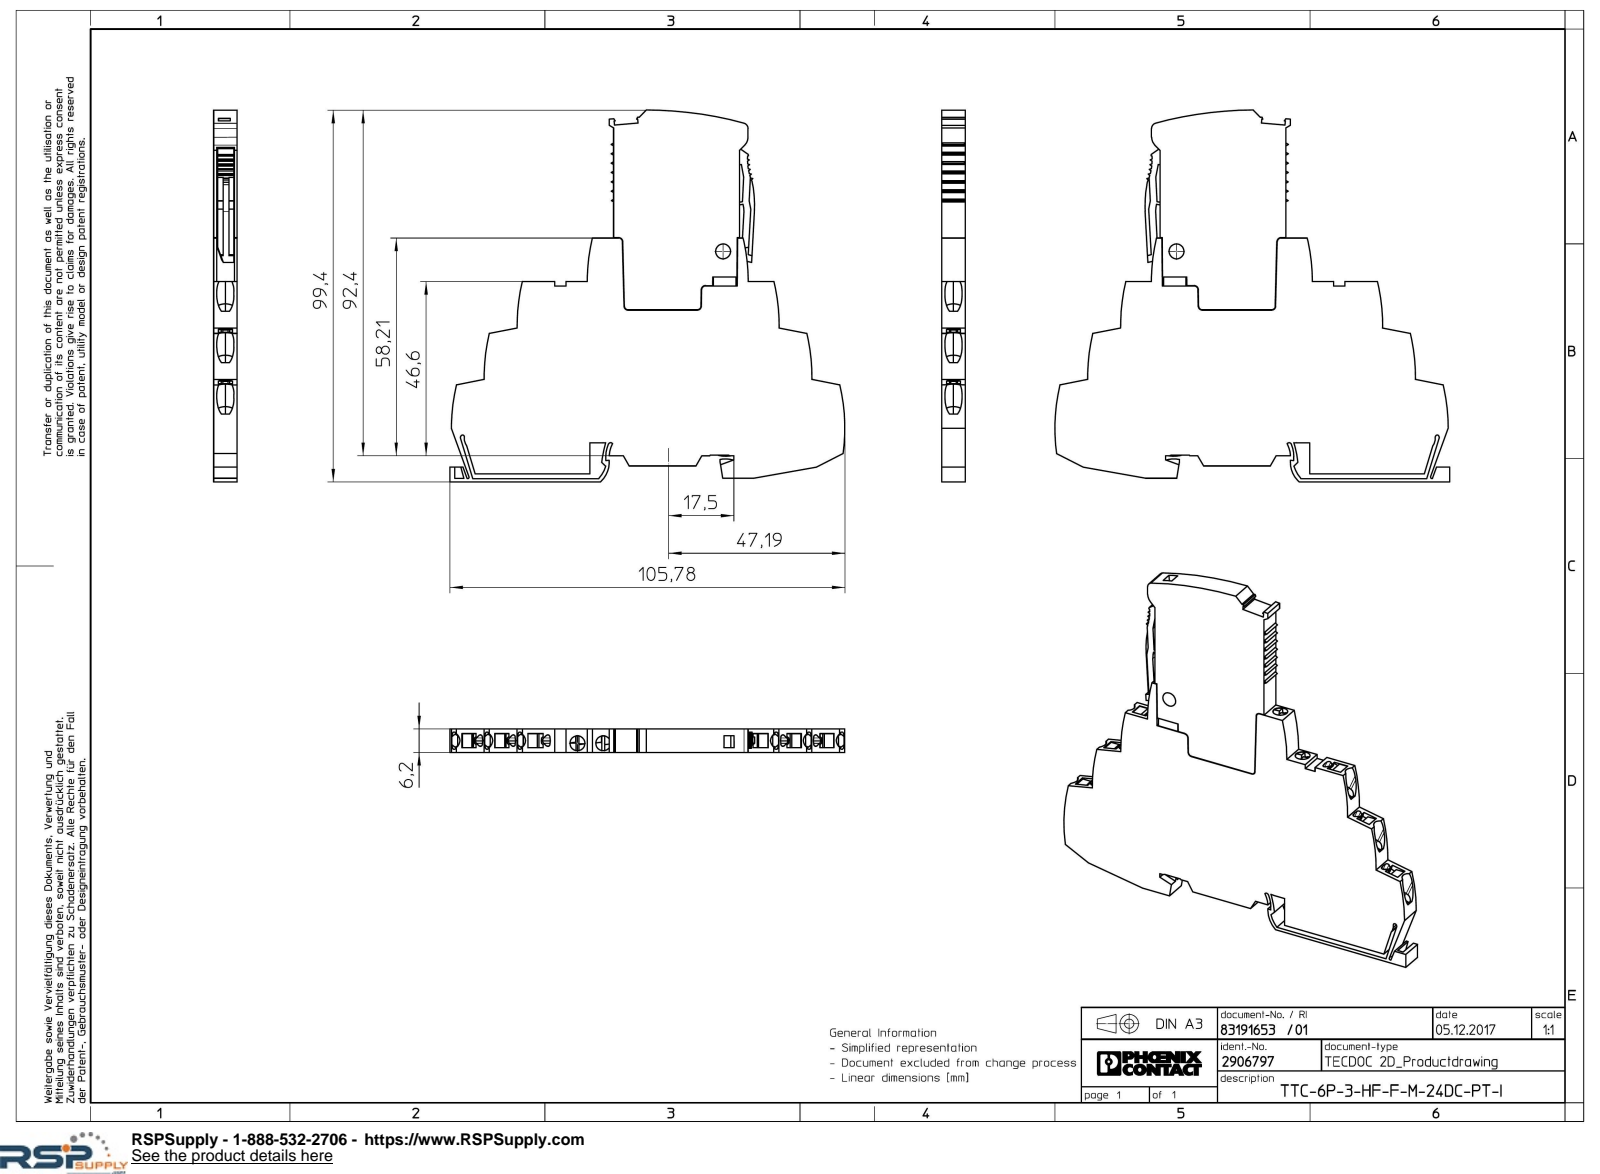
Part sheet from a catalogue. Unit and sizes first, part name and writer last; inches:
Units: inches
Overall size (bounding box): 4.165 × 3.913 × 0.248
Round holes (diameter × count): ⌀0.157 ×1
Partial cylindrical surfaces — rounded edges, fillets, slot ends (radius × count): R0.094 ×24, R0.02 ×20, R0.039 ×16, R0.031 ×12, R1.969 ×8, R0.07 ×6, R0.216 ×6, R0.035 ×2
Main face-to-face distances: 0.248, 0.035, 0.085, 0.05, 0.134, 0.084, 0.169, 0.033, 0.039, 0.183
Volume: 2.3 in³ · Surface area: 26.96 in²
Bodies: 1 solid, 500 faces (348 planar, 132 cylindrical, 20 other)
Part name (STEP PRODUCT): TTC_6P...M...PT-I-select
STEP written by: Creo Elements/Direct Modeling 20.1A 29-Sep-2018 (C) Parametric Technology GmbH (AUTOMOTIVE_DESIGN)
